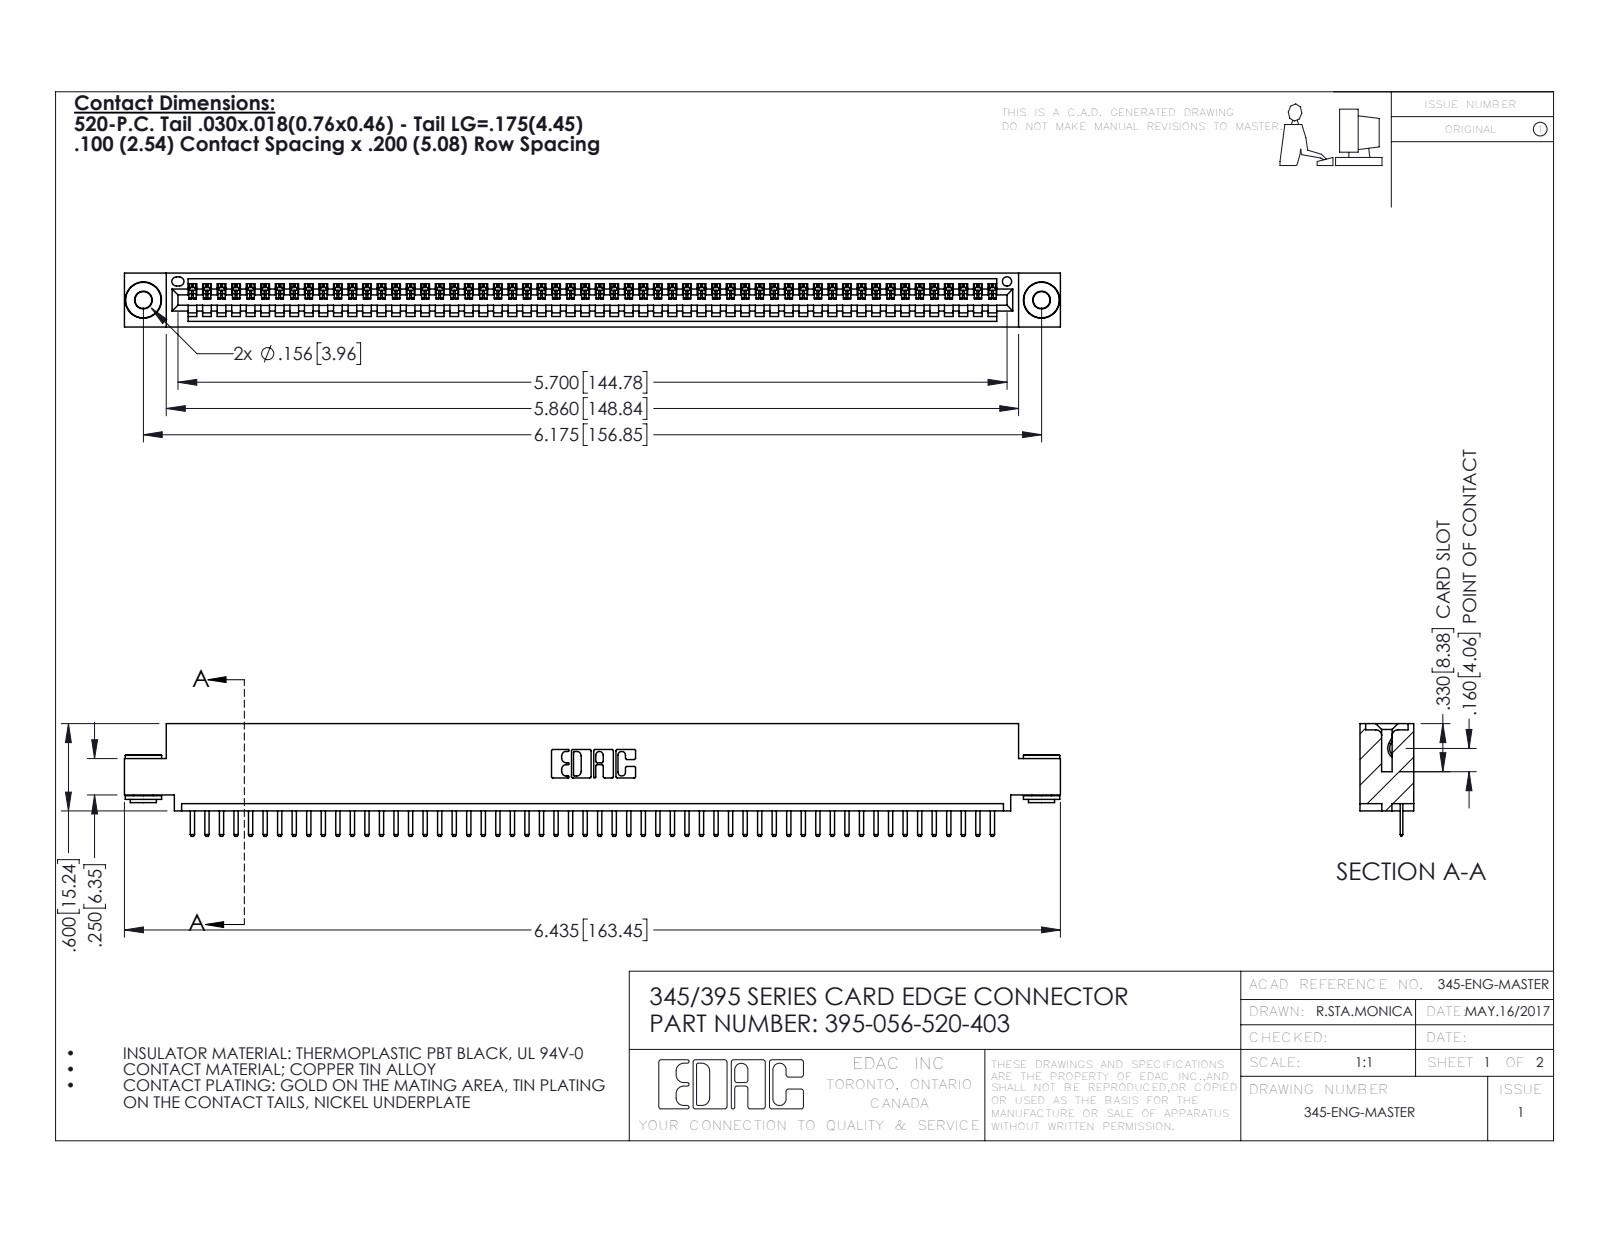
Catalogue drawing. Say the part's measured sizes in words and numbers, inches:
The part is named "345-292-001_345-293-120; 395-056-520-403; 345 Part_0.110 Offset - 0.156 Dia-TH; 345-250-002_345-250-002-102". Its 3-D file was written by "SolidWorks 2016 (CONFIG_CONTROL_DESIGN)". It is 59 solids with 3640 faces: 2446 planar, 1186 cylindrical and 8 other. Overall it measures 6.435 by 0.775 by 0.37 inches. Its volume is 0.941 cubic inches and its surface area 31.71 square inches. Round holes: 2 of diameter 0.116, 2 of diameter 0.156, 1 of diameter 0.064. Round bosses or shafts: 2 of diameter 0.25, 2 of diameter 0.18, 2 of diameter 0.136. Partial cylindrical surfaces (rounded edges, fillets, slot ends): 114 of radius 0.01, 112 of radius 0.006, 22 of radius 0.01, 6 of radius 0.007, 6 of radius 0.031, 3 of radius 0.026, 2 of radius 0.031, 2 of radius 0.04. The main face-to-face distances are 0.072, 0.298, 0.37, 0.2, 0.025, 0.098, 0.272, 0.225, 0.072, 0.149. The hole center spacings are 0.27, 5.939, 6.175.
